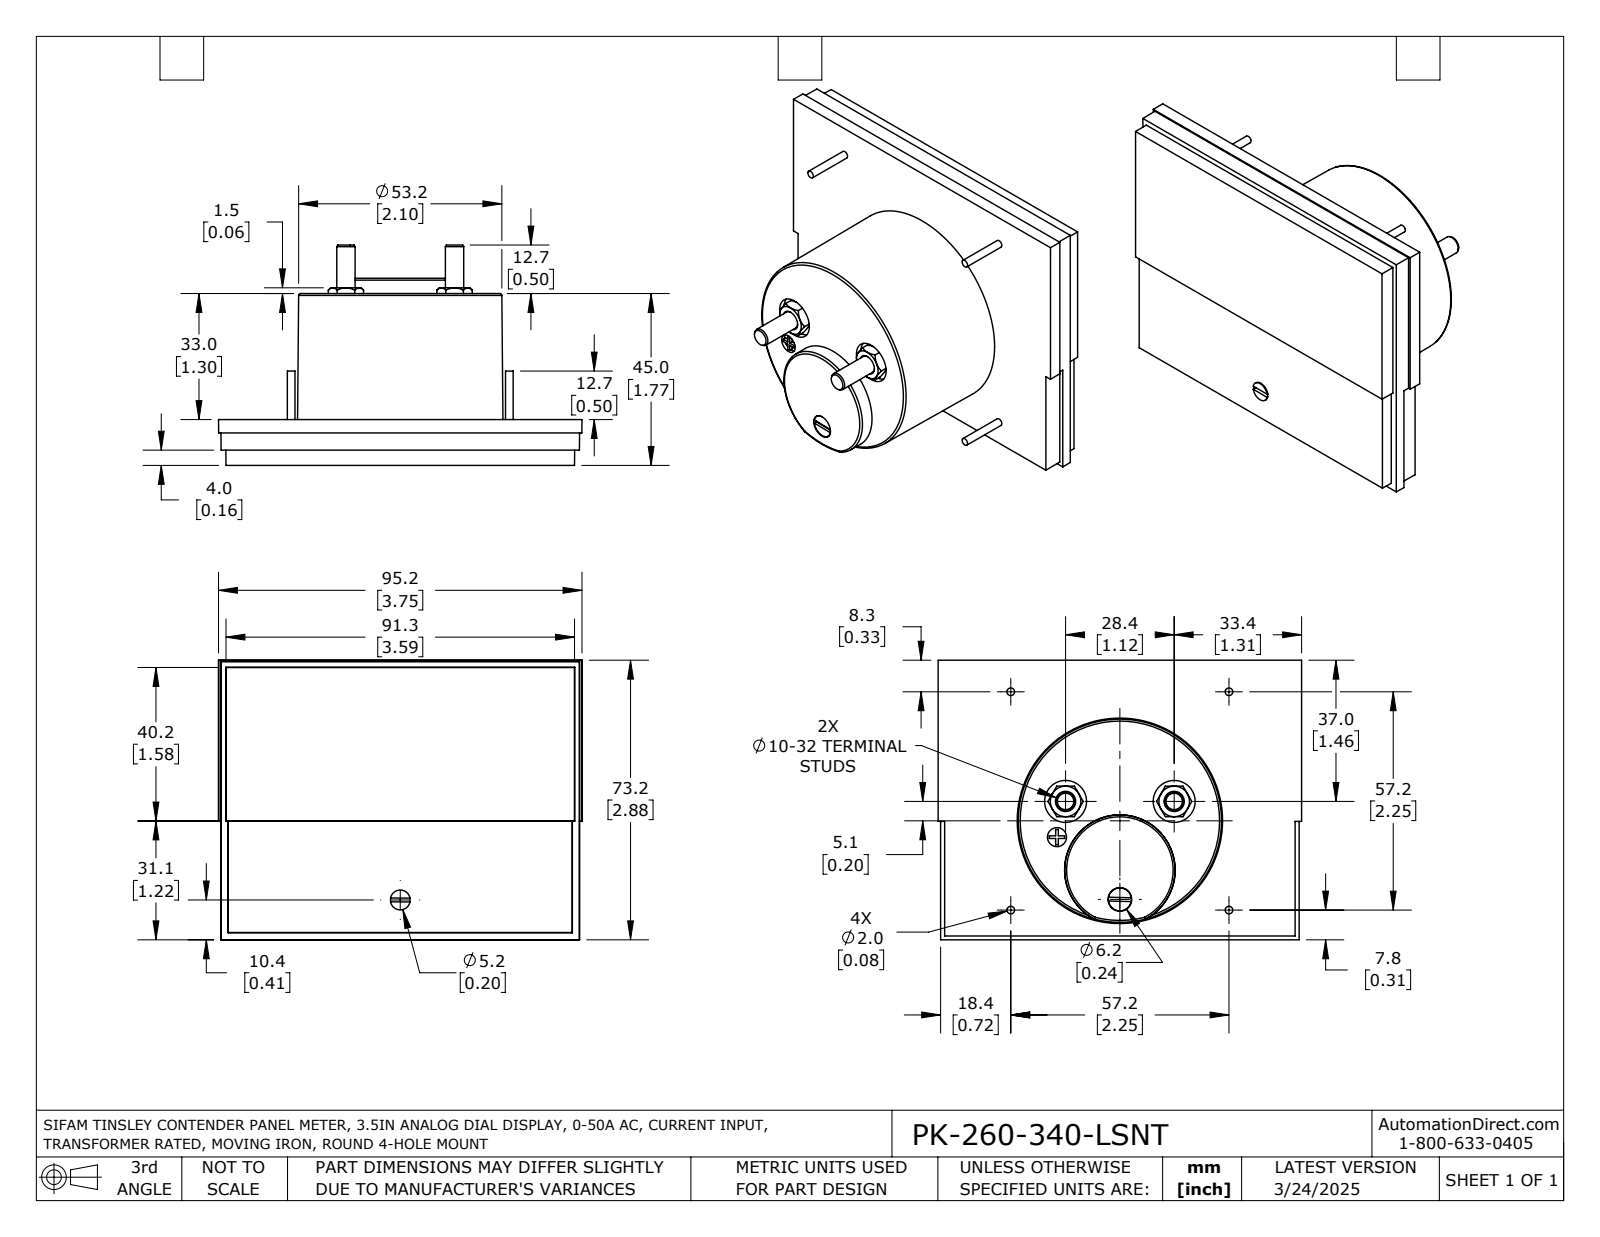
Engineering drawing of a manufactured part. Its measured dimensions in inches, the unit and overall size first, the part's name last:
Units: inches
Overall size (bounding box): 3.748 × 2.882 × 2.272
Round holes (diameter × count): ⌀0.433 ×2, ⌀0.197 ×1, ⌀0.244 ×1
Round bosses / shafts (diameter × count): ⌀0.079 ×4, ⌀0.189 ×2, ⌀0.236 ×1, ⌀0.205 ×1
Partial cylindrical surfaces — rounded edges, fillets, slot ends (radius × count): R0.1 ×1
Main face-to-face distances: 0.472, 0.03, 0.443, 1.772, 1.299, 1.742, 0.157, 0.073, 0.315, 1.457
Hole centre spacings: 1.155, 0.379, 0.912, 1.12, 1.263
Volume: 9.446 in³ · Surface area: 38.39 in²
Bodies: 1 solid, 163 faces (76 planar, 31 cylindrical, 56 other)
Part name (STEP PRODUCT): PK-260-340-LSNT
STEP written by: SolidWorks 2021 (AUTOMOTIVE_DESIGN)
